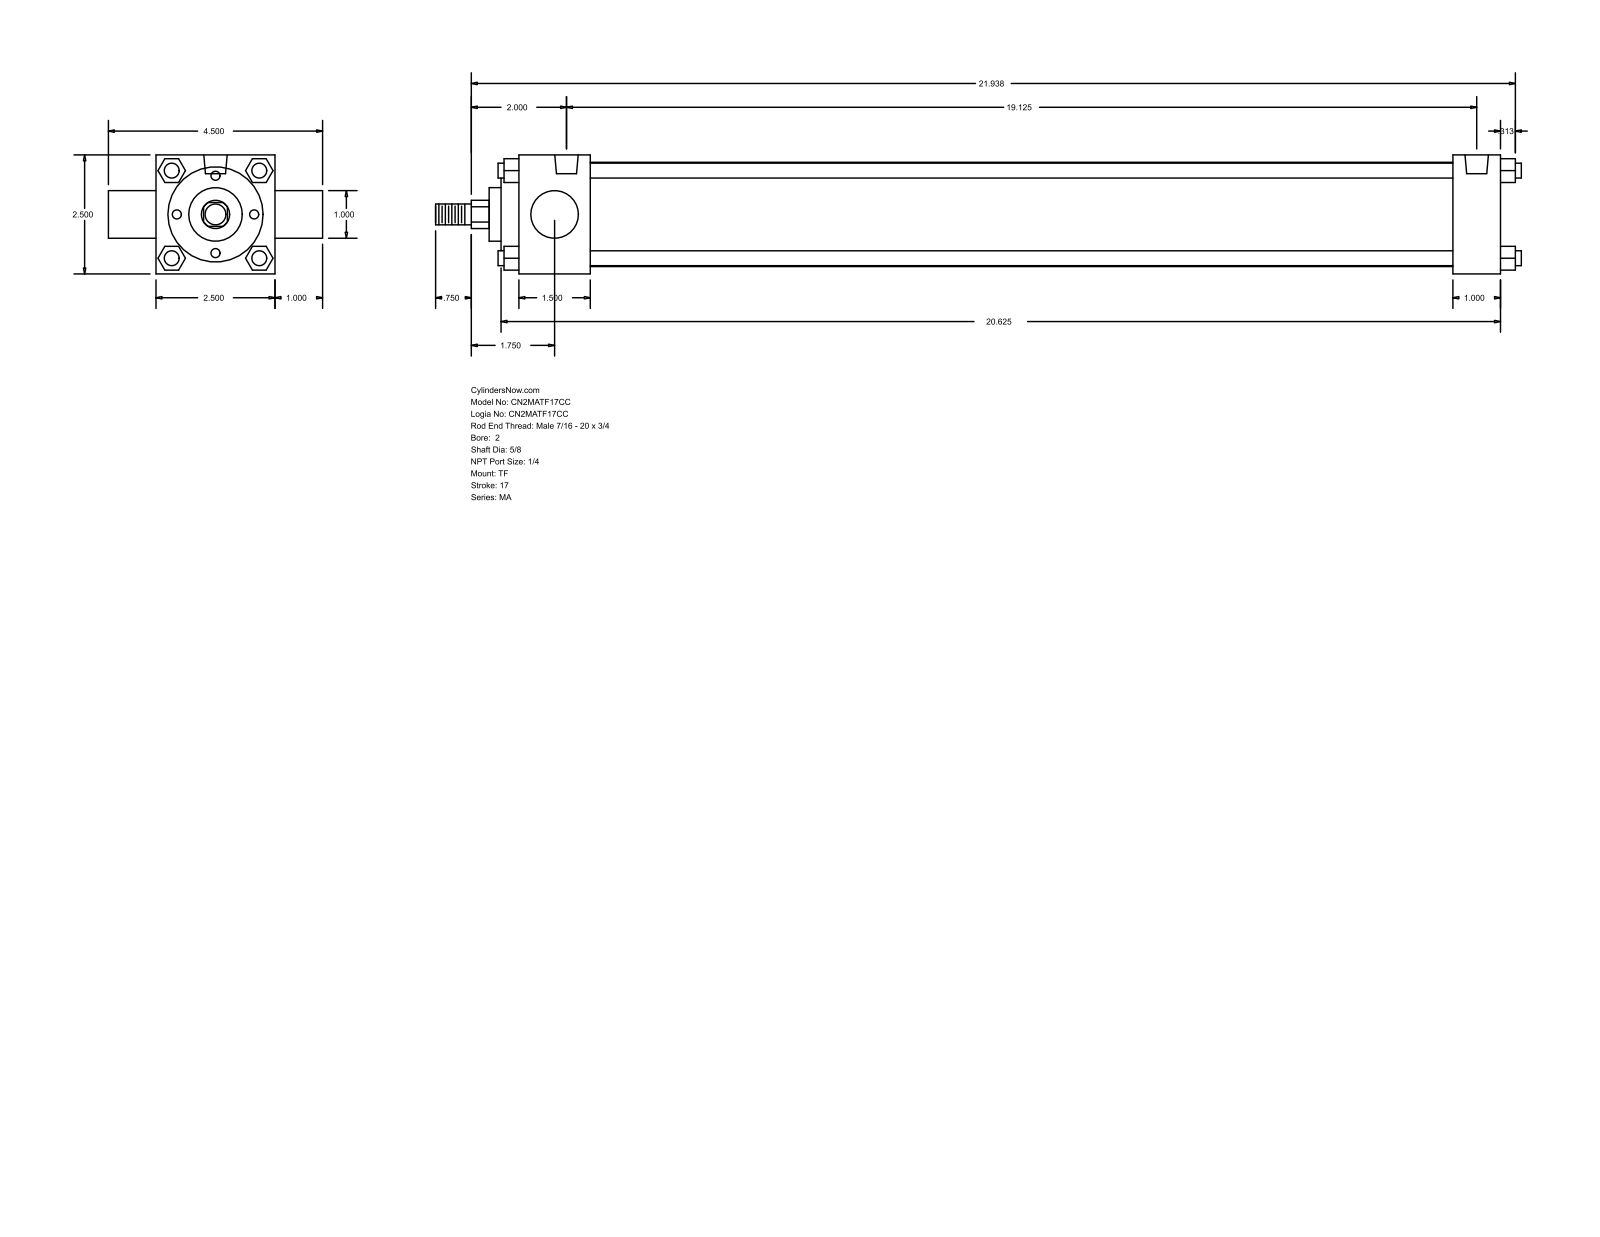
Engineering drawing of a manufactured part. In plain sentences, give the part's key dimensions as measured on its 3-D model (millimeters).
The part is named "MA_TF__0200_0.625". Its 3-D file was written by "GSSL Pune (CONFIG_CONTROL_DESIGN)". It is 0 solids with 122 faces: 93 planar, 29 cylindrical and 0 other. Overall it measures 579.44 by 114.3 by 63.5 millimeters. Round holes: 3 of diameter 7.94, 2 of diameter 12.49. Round bosses or shafts: 4 of diameter 7.94, 1 of diameter 55.63, 1 of diameter 50.8, 1 of diameter 28.57, 1 of diameter 25.4, 1 of diameter 15.88, 1 of diameter 11.11. Partial cylindrical surfaces (rounded edges, fillets, slot ends): 1 of radius 7.54. The main face-to-face distances are 63.5, 38.1, 12.7, 523.87, 498.48, 460.38, 485.77, 25.39, 9.52, 47.62. The hole center spacings are 485.78.
